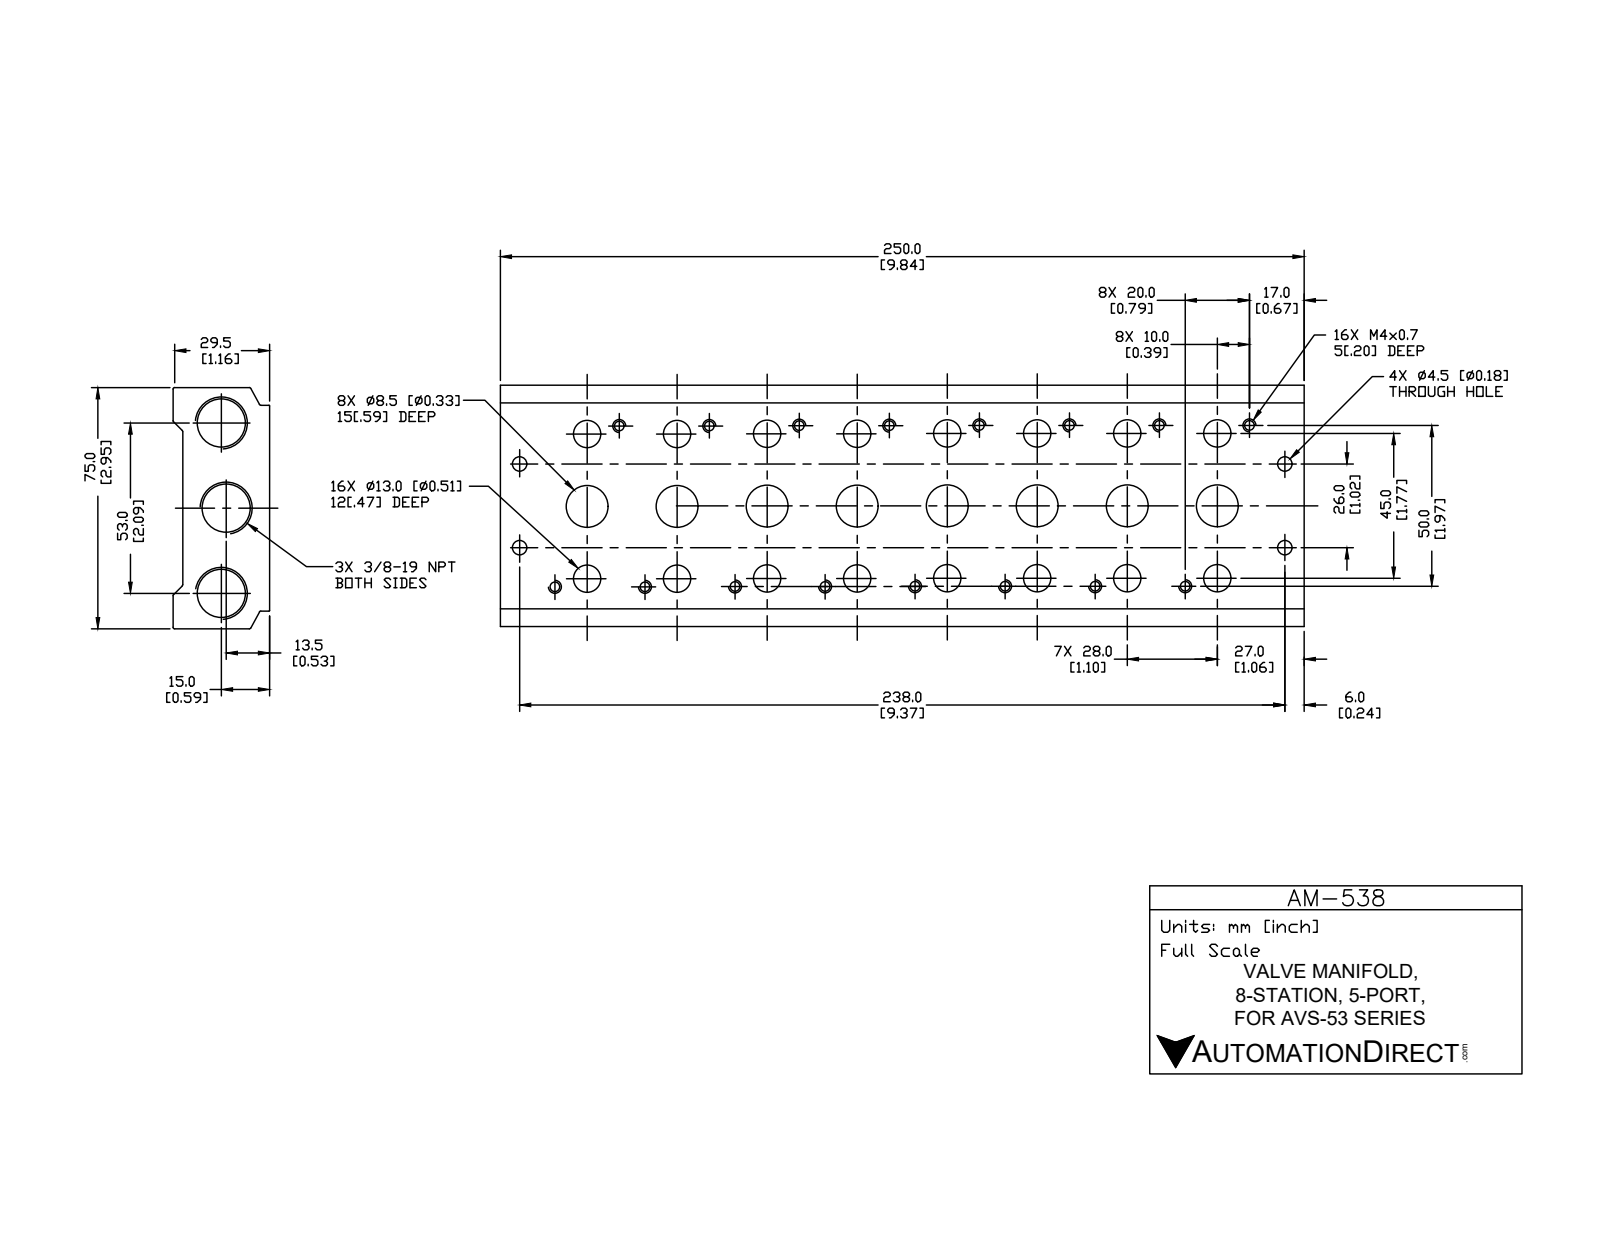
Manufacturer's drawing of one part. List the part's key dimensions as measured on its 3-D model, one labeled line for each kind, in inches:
Part name (STEP PRODUCT): AM-538
STEP written by: SolidWorks 2015 (CONFIG_CONTROL_DESIGN)
Units: inches
Bodies: 1 solid, 201 faces (52 planar, 105 cylindrical, 44 other)
Overall size (bounding box): 9.843 × 2.953 × 1.181
Volume: 22.84 in³ · Surface area: 147.1 in²
Round holes (diameter × count): ⌀0.13 ×16, ⌀0.335 ×16, ⌀0.512 ×8, ⌀0.177 ×4, ⌀0.562 ×3
Partial cylindrical surfaces — rounded edges, fillets, slot ends (radius × count): R0.02 ×11
Main face-to-face distances: 1.063, 2.953, 0.118, 1.181, 9.843, 0.236, 2.717, 0.407, 9.436, 0.787
Hole centre spacings: 1.102, 2.205, 0.406, 1.911, 3.307, 4.409, 5.512, 2.087
